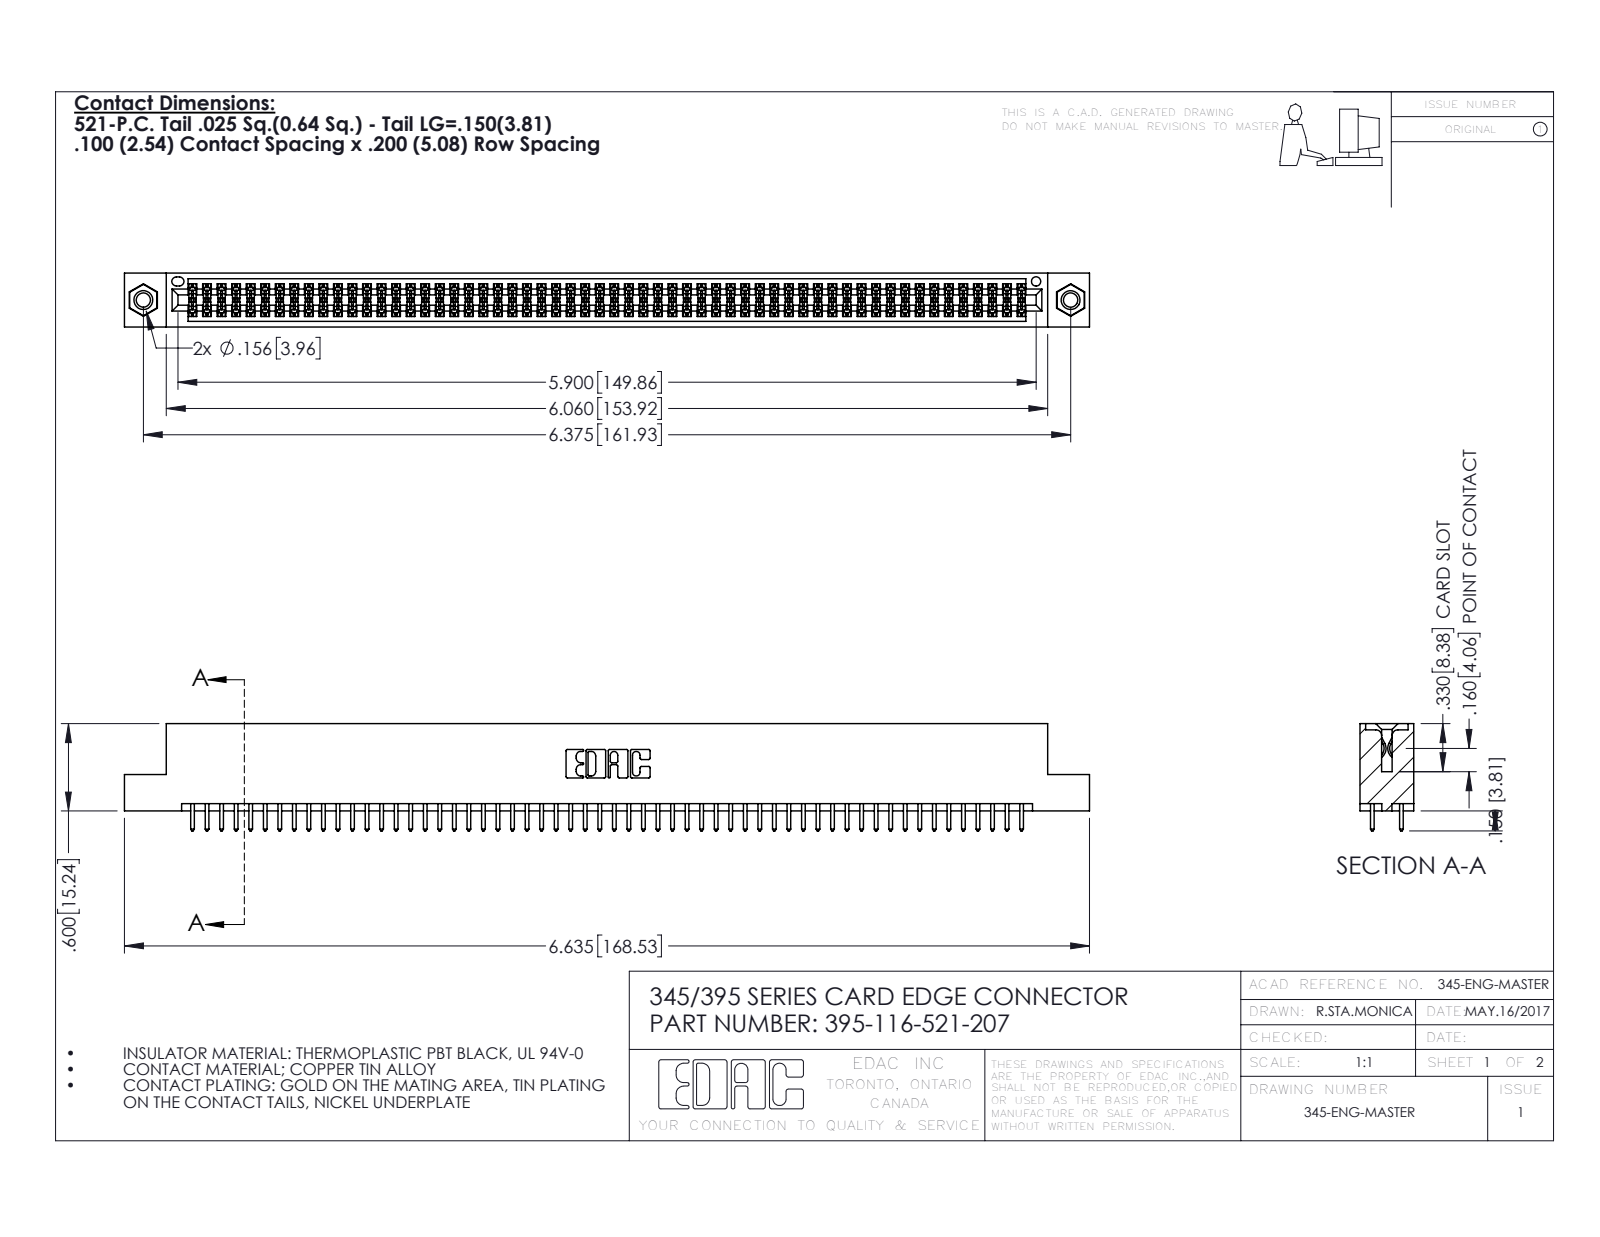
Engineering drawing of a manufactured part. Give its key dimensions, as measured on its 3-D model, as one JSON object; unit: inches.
{"part_name": "345-250-001_345-250-005-103; 345 Part_Flush Mounting Lugs - 0.156 Dia-TI; 345-292-001_345-293-121; 395-116-521-207", "step_written_by": "SolidWorks 2016 (CONFIG_CONTROL_DESIGN)", "units": "inches", "bodies": {"solids": 119, "faces": 5986, "planar": 3940, "cylindrical": 2030, "other": 16}, "overall_size": [6.635, 0.737, 0.37], "volume_in3": 1.004, "surface_area_in2": 37.76, "round_holes": [[0.098, 2], [0.125, 2], [0.156, 2], [0.064, 1]], "round_bosses_or_shafts": [[0.155, 2]], "partial_cylinders_radius": [[0.006, 174], [0.01, 116], [0.01, 22], [0.007, 6], [0.031, 6], [0.026, 3], [0.014, 2], [0.019, 2]], "face_to_face_distances": [0.072, 0.298, 0.2, 0.098, 0.272, 0.025, 0.37, 0.225, 0.175, 0.149], "hole_center_spacings": [0.27, 6.139, 6.375]}
